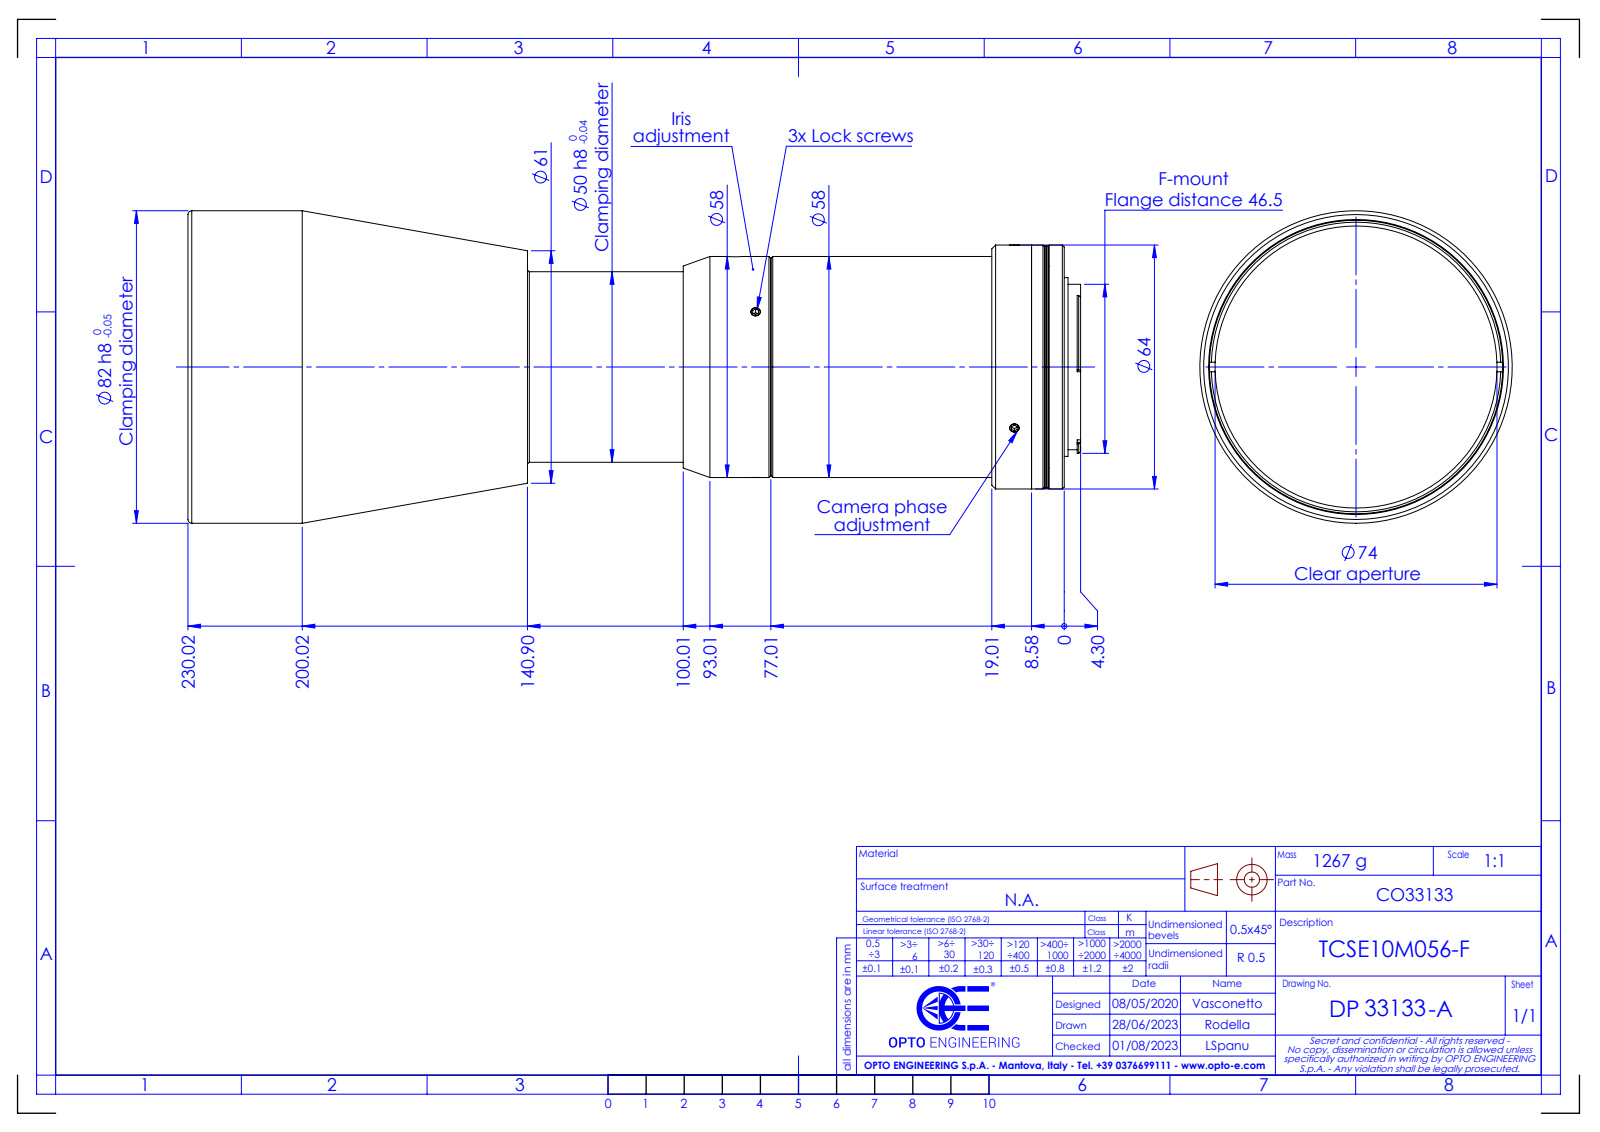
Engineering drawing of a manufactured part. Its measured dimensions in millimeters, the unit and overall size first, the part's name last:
Units: millimetres
Overall size (bounding box): 234.32 × 82 × 82
Round holes (diameter × count): ⌀4.2 ×1, ⌀42 ×1, ⌀45 ×1, ⌀74 ×1, ⌀77 ×1
Round bosses / shafts (diameter × count): ⌀82 ×1, ⌀64 ×1, ⌀63.5 ×1, ⌀58 ×1, ⌀50 ×1, ⌀46.9 ×1, ⌀43.4 ×1
Partial cylindrical surfaces — rounded edges, fillets, slot ends (radius × count): R0.5 ×6, R1.15 ×2, R22.65 ×1
Main face-to-face distances: 77.01, 71.44, 5.57, 73.01, 1.57, 4, 58, 13.44, 15.01, 19.01
Bodies: 0 solids, 167 faces (78 planar, 47 cylindrical, 42 other)
Part name (STEP PRODUCT): DP33133-A_TCSE10M056-F
STEP written by: SolidWorks 2021 (CONFIG_CONTROL_DESIGN)
